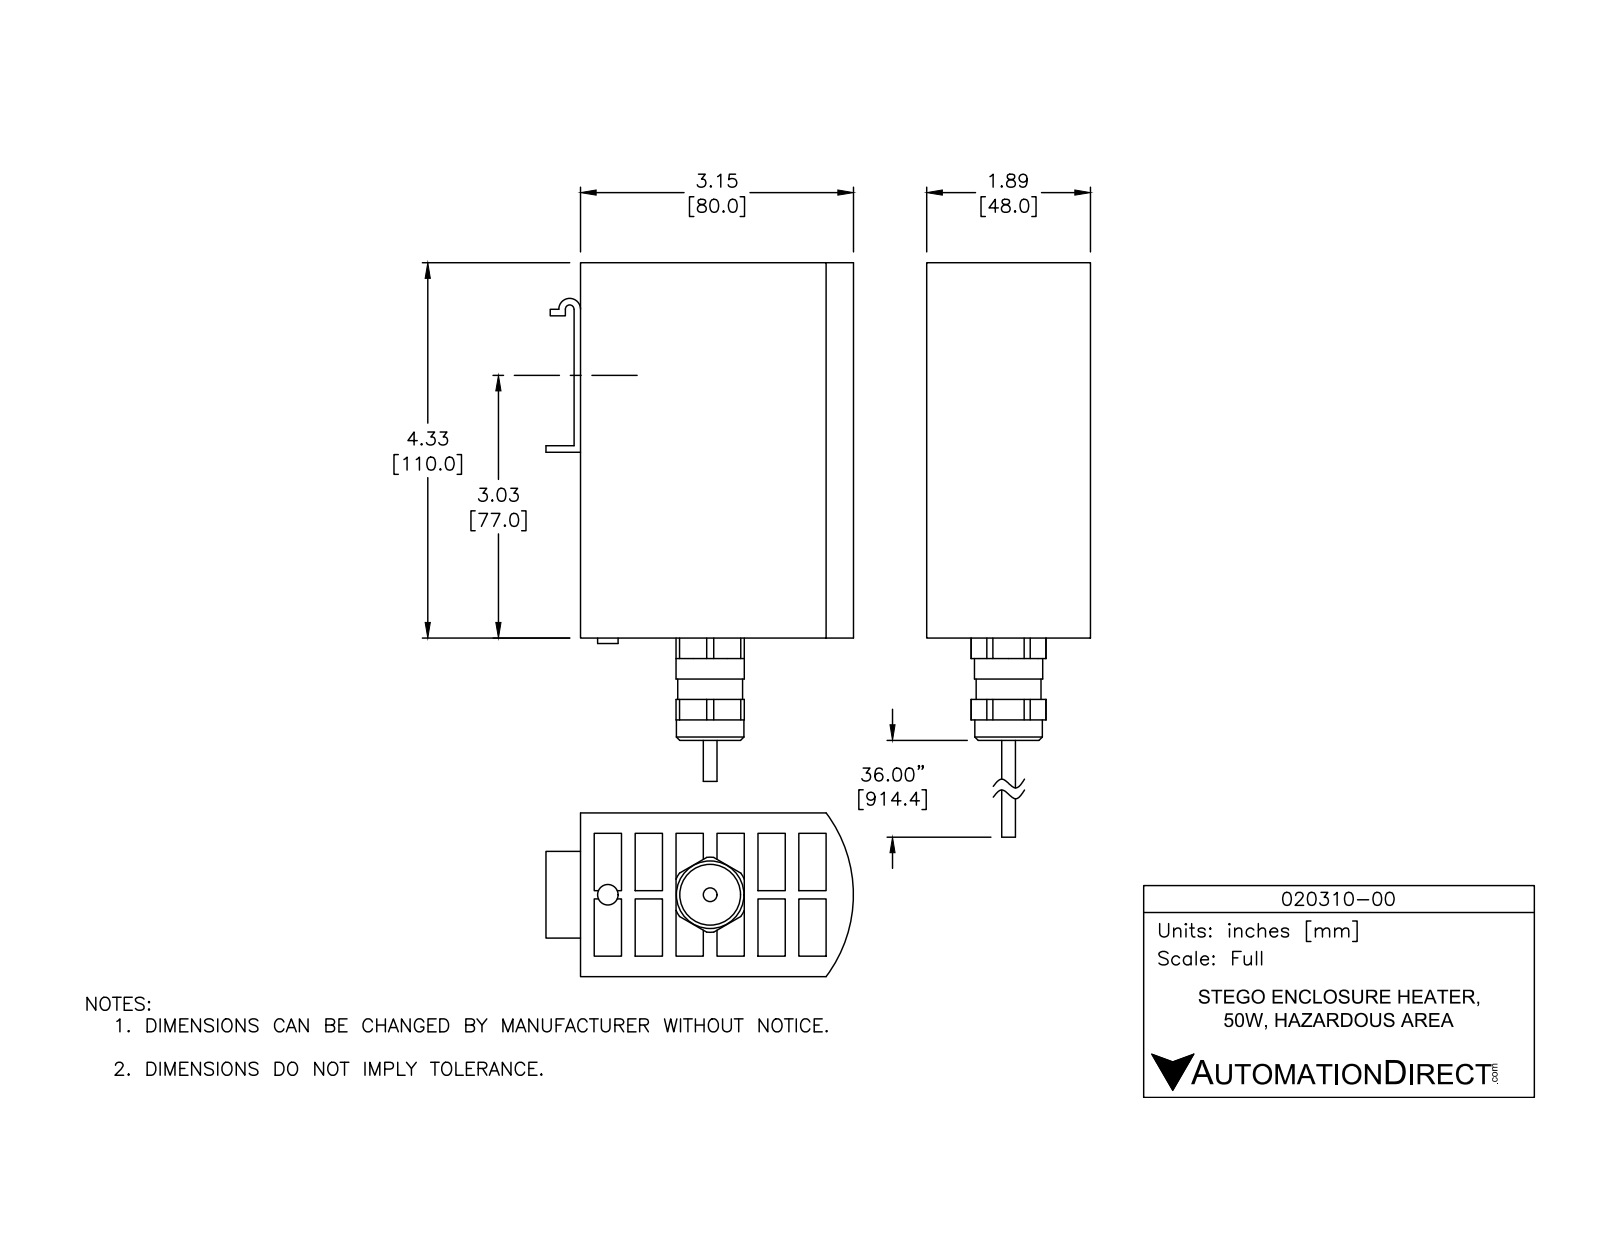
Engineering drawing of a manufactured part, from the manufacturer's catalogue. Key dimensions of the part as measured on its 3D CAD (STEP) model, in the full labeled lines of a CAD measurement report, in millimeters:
Part name (STEP PRODUCT): 020310-00
STEP written by: SolidWorks 2017 (AUTOMOTIVE_DESIGN)
Units: millimetres
Bodies: 3 solids, 125 faces (109 planar, 14 cylindrical, 2 other)
Overall size (bounding box): 151.9 × 90.2 × 48
Volume: 250 400 mm³ · Surface area: 99 940 mm²
Round bosses / shafts (diameter × count): ⌀20 ×1, ⌀19 ×1, ⌀4.1 ×1
Partial cylindrical surfaces — rounded edges, fillets, slot ends (radius × count): R1.3 ×1, R3.2 ×1, R40 ×1
Main face-to-face distances: 12, 24, 36, 48, 4, 8, 20, 16, 28, 32
